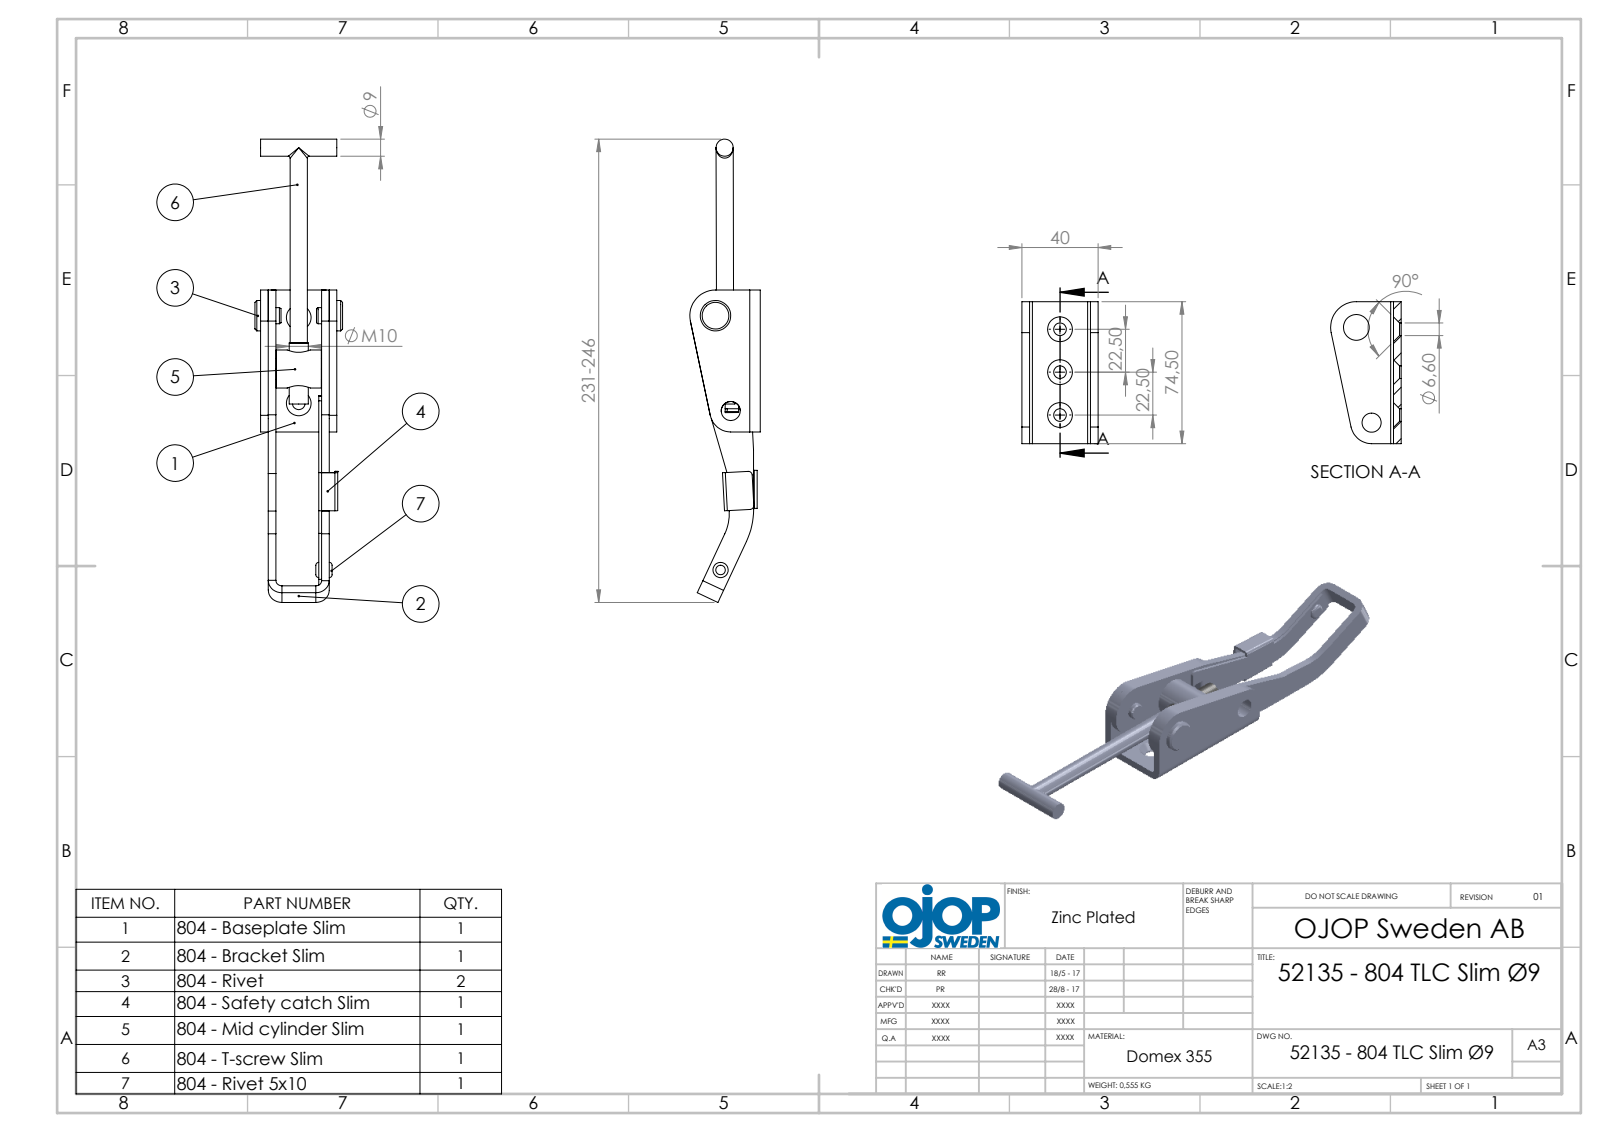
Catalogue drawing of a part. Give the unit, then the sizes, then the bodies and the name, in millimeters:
Units: millimetres
Overall size (bounding box): 243.13 × 46 × 37
Round holes (diameter × count): ⌀6.6 ×3, ⌀10 ×2, ⌀4.97 ×1, ⌀5.1 ×1, ⌀8.6 ×1, ⌀9.3 ×1, ⌀11.2 ×1, ⌀13.5 ×1
Round bosses / shafts (diameter × count): ⌀9 ×2, ⌀20 ×1, ⌀16 ×1, ⌀11 ×1, ⌀10.9 ×1, ⌀10 ×1, ⌀8.5 ×1, ⌀5 ×1
Partial cylindrical surfaces — rounded edges, fillets, slot ends (radius × count): R1.5 ×6, R0.5 ×4, R2 ×4, R5.5 ×2, R3 ×1, R3.17 ×1, R7 ×1, R7.17 ×1
Main face-to-face distances: 4, 32, 28, 8, 36, 24, 1.5, 40, 5.5, 30.5
Hole centre spacings: 22.5, 22.24, 22.27, 28.41, 45, 50.64, 50.67, 83.58
Volume: 71 465 mm³ · Surface area: 43 926 mm²
Bodies: 8 solids, 208 faces (88 planar, 92 cylindrical, 28 other)
Part name (STEP PRODUCT): 72297 - Platta 804 Slim; 72139 - Bygel 804 Slim; 62035 - Ansatsnit 10,9x5,7x8,5x8,0 FZB(804); 72093 - T-skruv 804 Slim (+4 more)
STEP written by: SolidWorks 2015 (AUTOMOTIVE_DESIGN)
